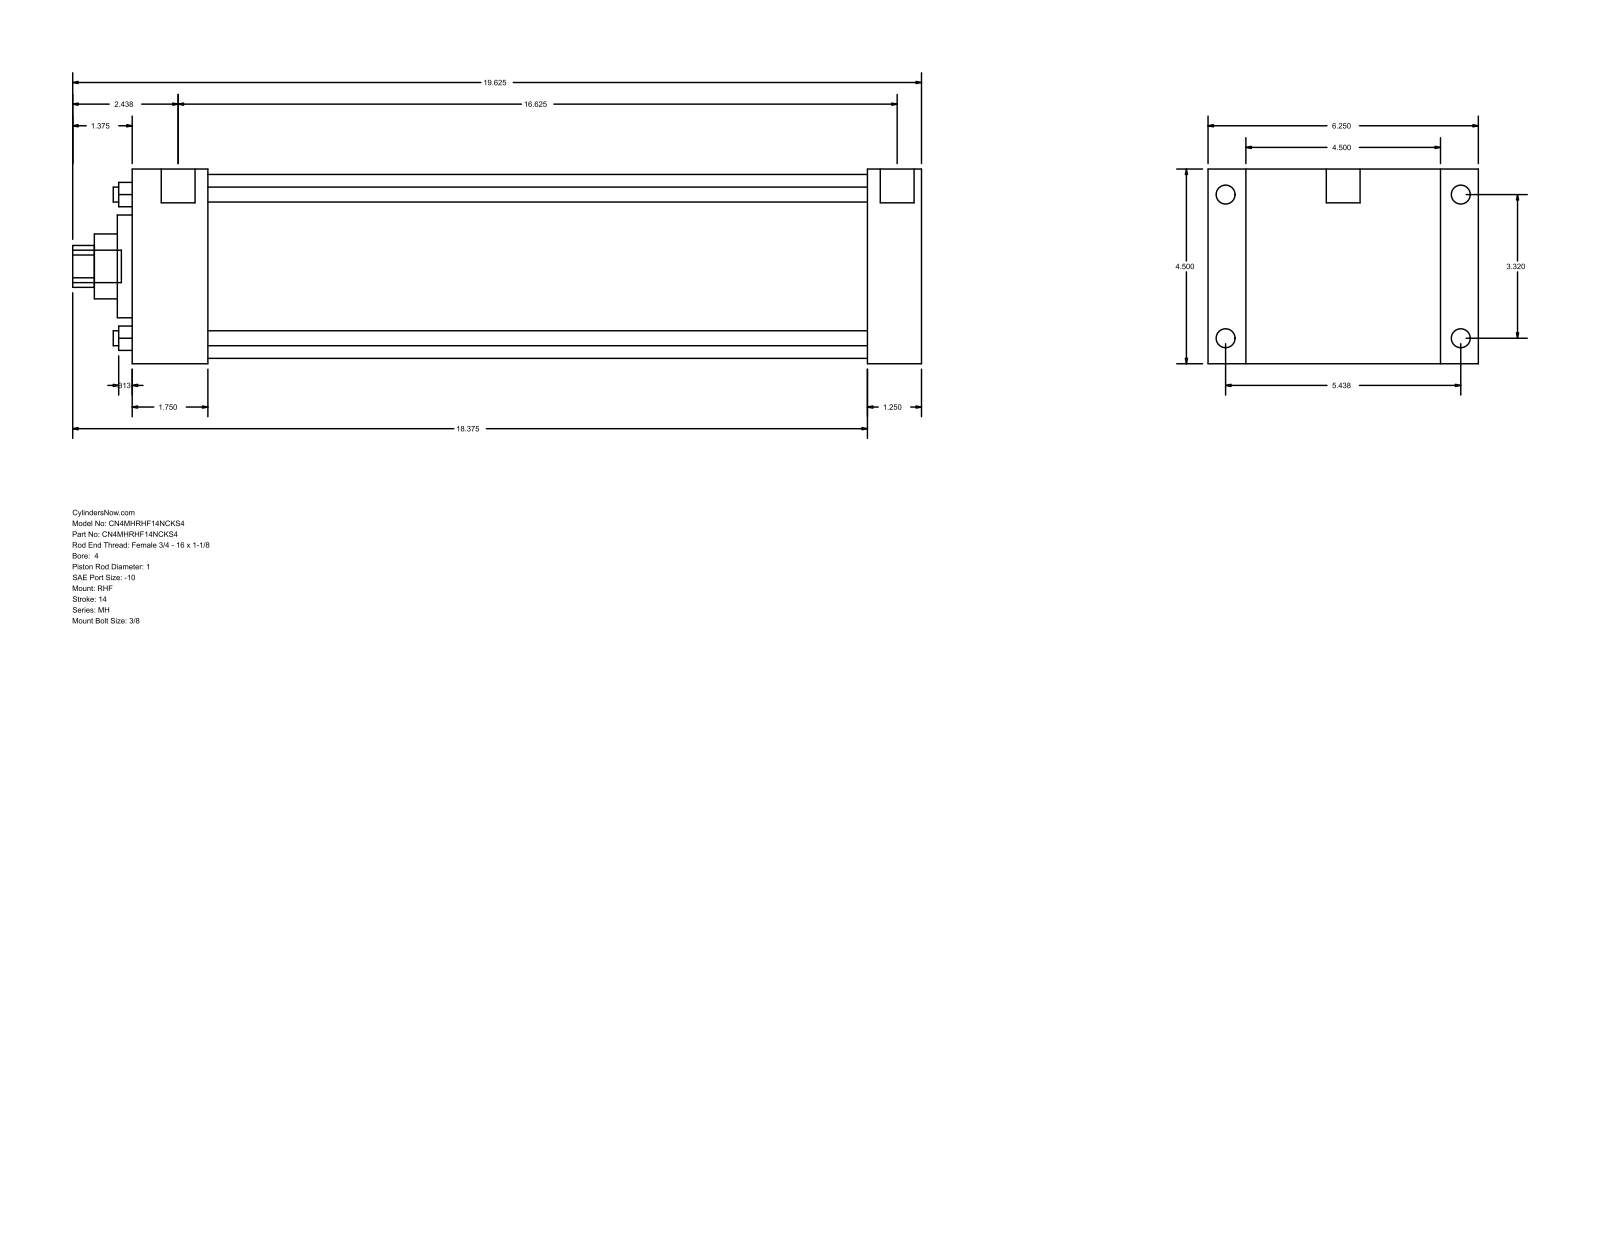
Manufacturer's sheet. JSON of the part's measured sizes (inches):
{"part_name": "MH_RHF__0400_1", "step_written_by": "GSSL Pune (CONFIG_CONTROL_DESIGN)", "units": "inches", "bodies": {"solids": 0, "faces": 90, "planar": 61, "cylindrical": 29, "other": 0}, "overall_size": [19.625, 6.25, 4.5], "round_holes": [[0.345, 4], [1, 1], [1.5, 1], [2.375, 1], [4.25, 1]], "round_bosses_or_shafts": [[0.438, 4], [0.344, 4], [0.781, 2], [0.75, 1]], "partial_cylinders_radius": [[0.484, 1]], "face_to_face_distances": [4.5, 18.25, 17, 1.25, 0.875, 5.375, 1.75, 15.25, 16.5, 6.25], "hole_center_spacings": [2.347, 3.32, 4.695]}
